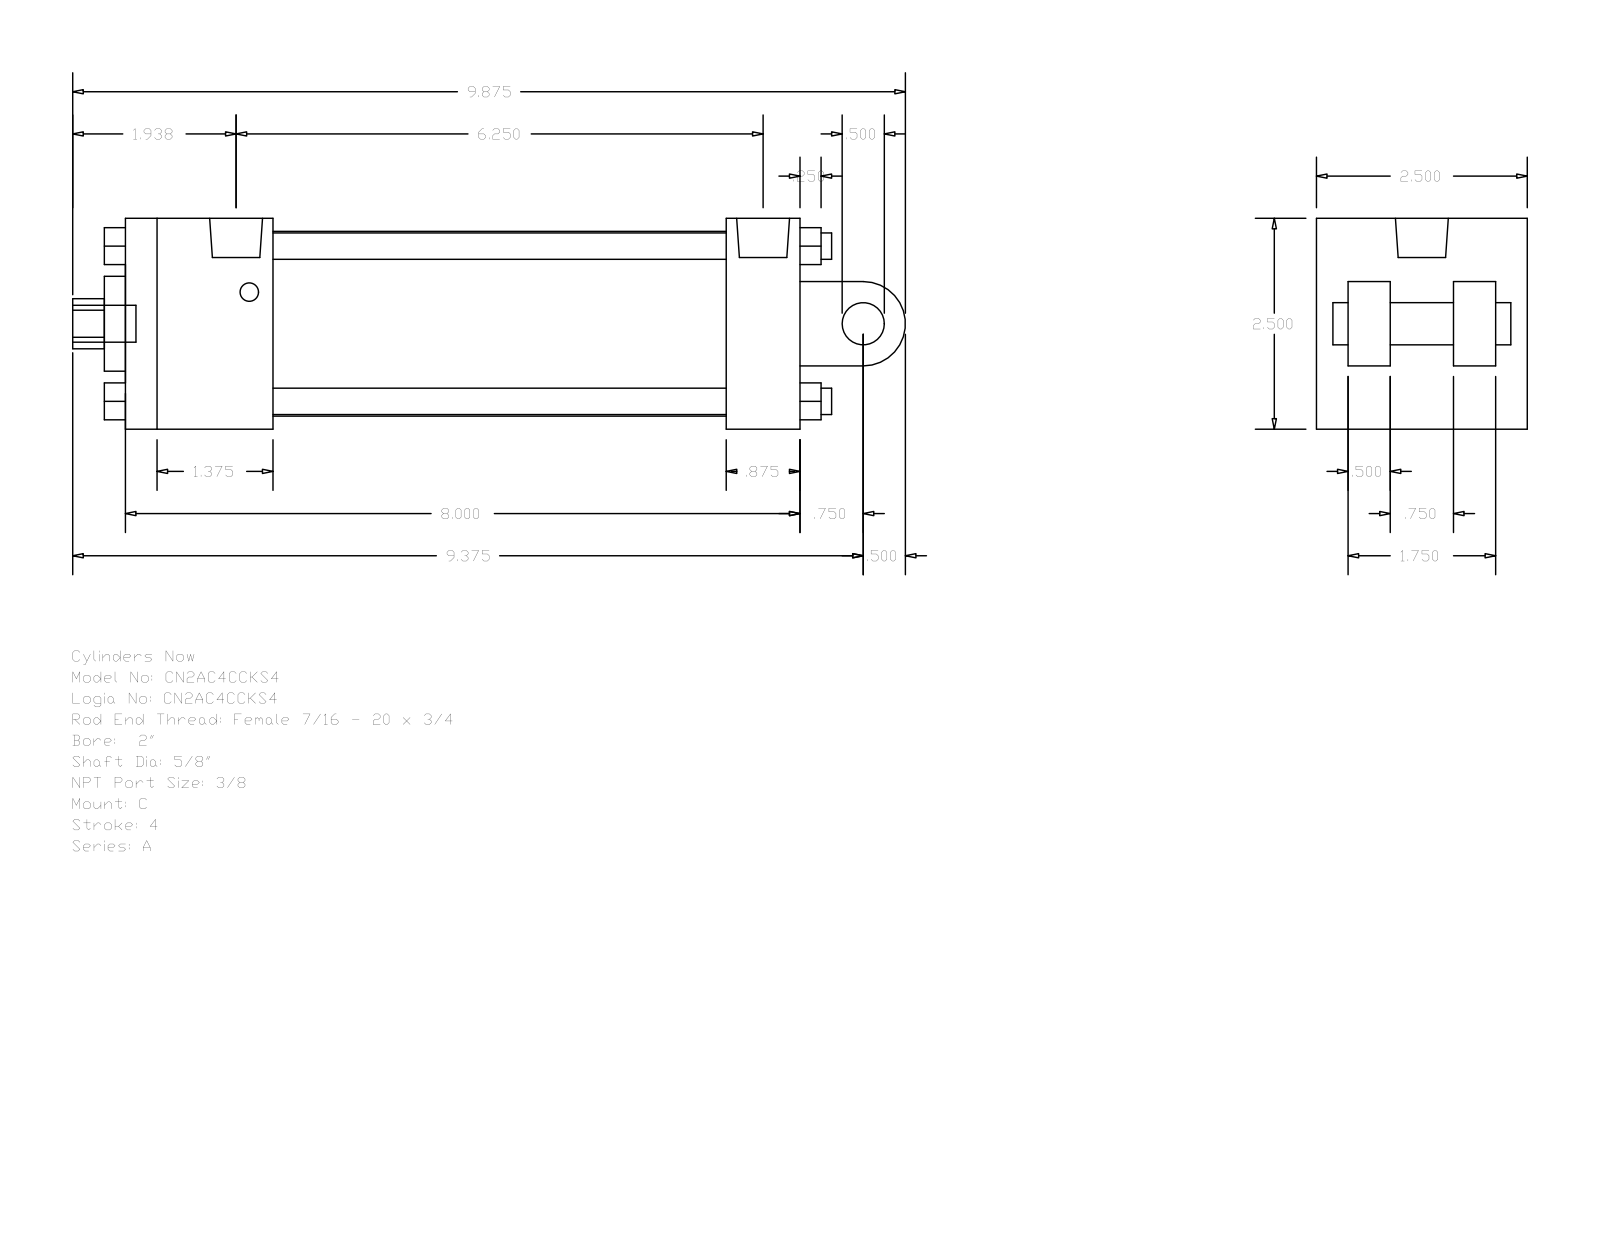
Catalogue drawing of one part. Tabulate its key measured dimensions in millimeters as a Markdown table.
| quantity | value |
| --- | --- |
| part name | A_C__0200_0.625 |
| STEP written by | GSSL Pune (CONFIG_CONTROL_DESIGN) |
| units | millimeters |
| bodies | 0 solids, 135 faces (102 planar, 33 cylindrical, 0 other) |
| overall size | 250.82 × 63.5 × 63.5 |
| round holes (diameter × count) | 5.56 × 2, 15.88 × 1, 15.93 × 1, 28.57 × 1, 55.63 × 1 |
| round bosses / shafts (diameter × count) | 7.94 × 4, 5.56 × 2, 15.93 × 1, 12.7 × 1, 11.11 × 1 |
| partial cylindrical surfaces (radius × count) | 7.54 × 1, 12.7 × 1 |
| main face-to-face distances | 63.5, 203.19, 22.22, 44.45, 158.74, 180.97, 136.52, 12.7, 41.28, 9.52 |
| hole center spacings | 3.97 |
